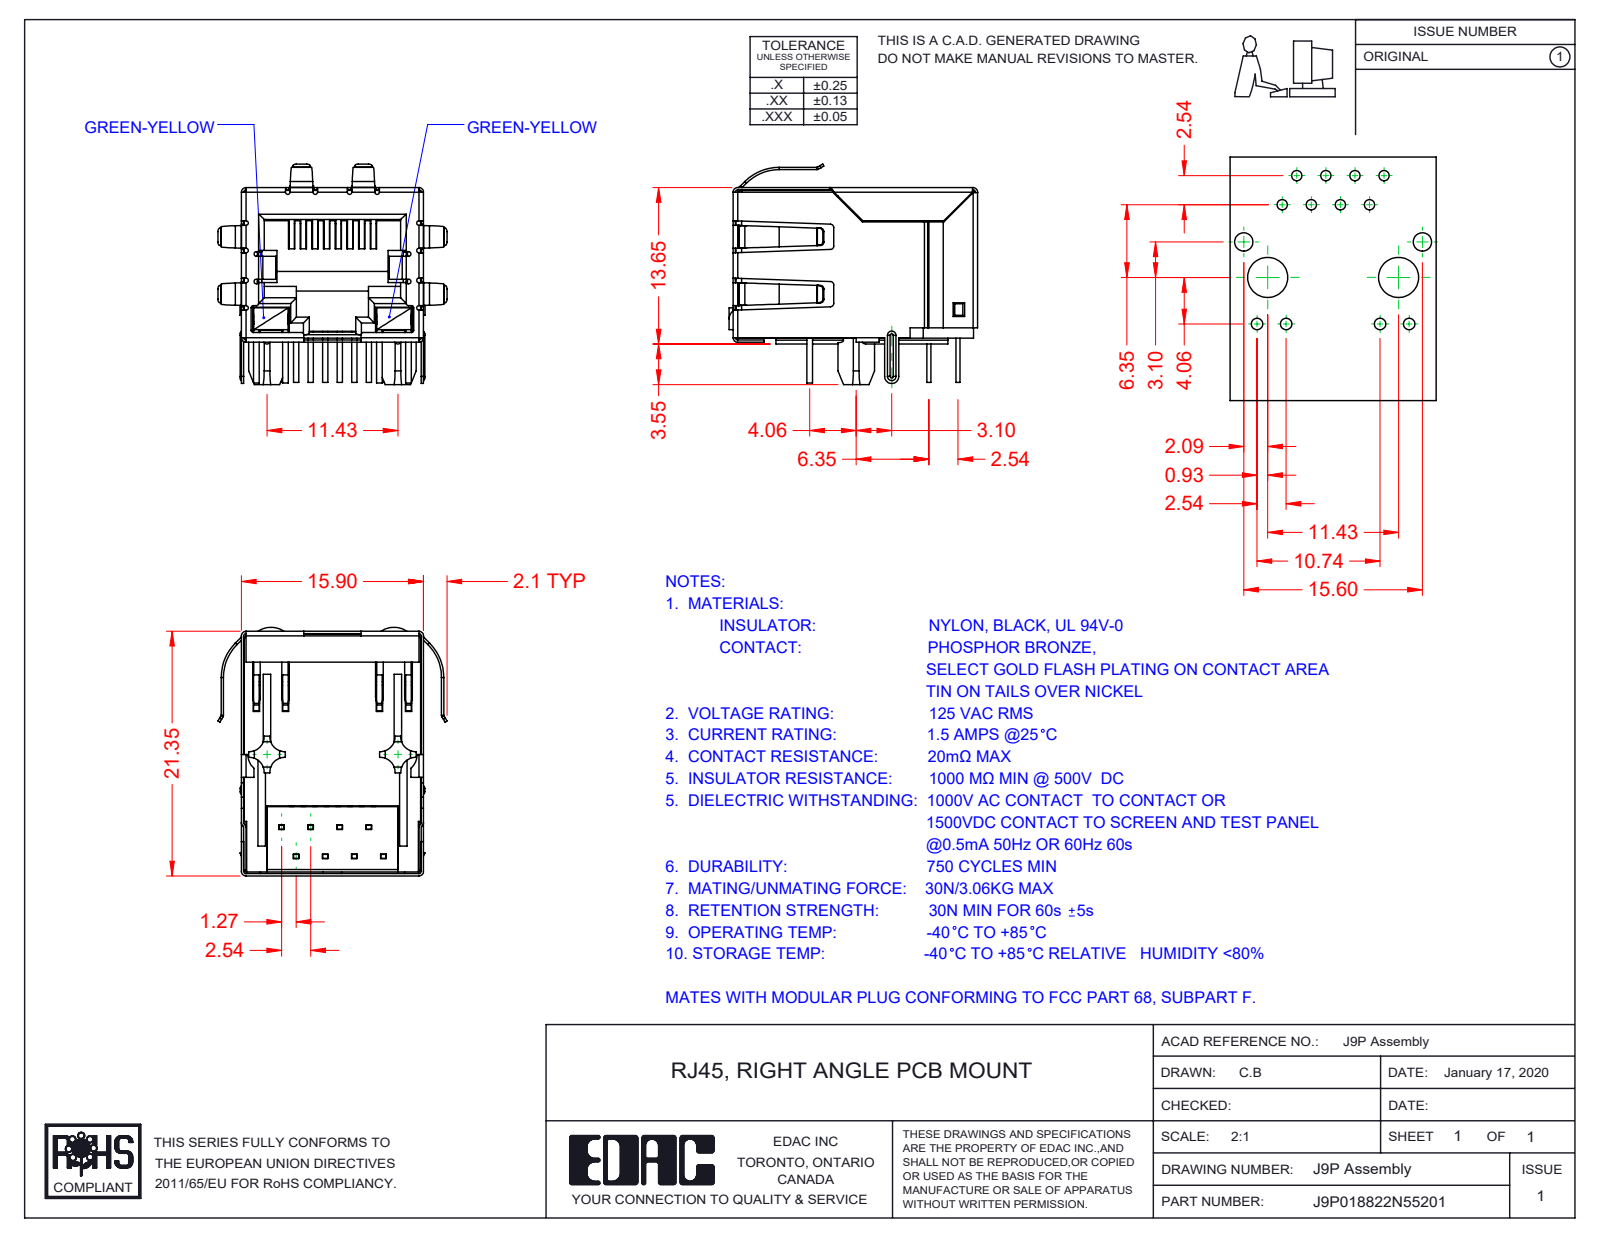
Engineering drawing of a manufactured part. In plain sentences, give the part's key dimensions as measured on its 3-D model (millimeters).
The part is named "9P-LED Insulator; 9P-LED LED LH_5-Green-Yellow; 9P-LED Assembly; 9P-LED LED RH_5-Green-Yellow (+4 more)". Its 3-D file was written by "SolidWorks 2016 (CONFIG_CONTROL_DESIGN)". It is 13 solids with 1476 faces: 1042 planar, 340 cylindrical and 94 other. Overall it measures 21.7 by 20 by 19.25 millimeters. Its volume is 2 687 cubic millimeters and its surface area 7 515 square millimeters. Partial cylindrical surfaces (rounded edges, fillets, slot ends): 39 of radius 0.2, 22 of radius 0.5, 20 of radius 0.3, 16 of radius 0.4, 8 of radius 1.3, 5 of radius 0.23, 4 of radius 0.11, 4 of radius 0.31. The main face-to-face distances are 15.45, 15.7, 15.65, 0.35, 0.54, 15.5, 12.36, 0.6, 1.4, 0.59.
